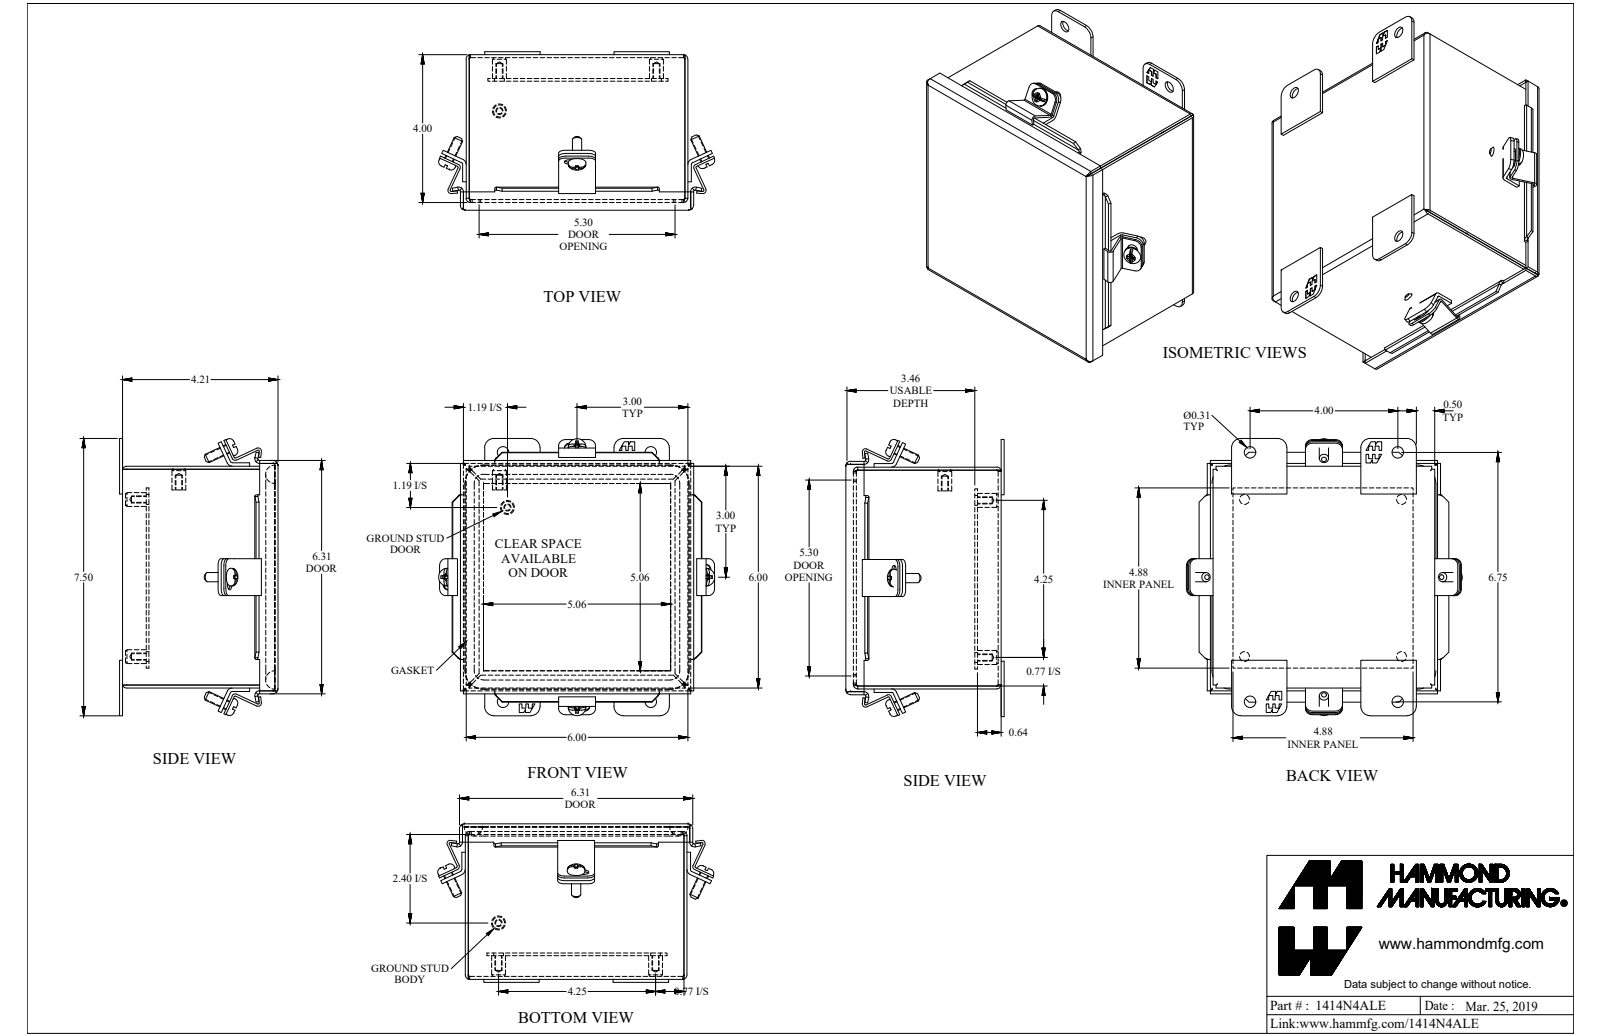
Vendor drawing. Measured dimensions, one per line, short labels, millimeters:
name: 1414N4ALE
written by: SolidWorks 2018 (AUTOMOTIVE_DESIGN)
unit: mm
bodies: 26 solids, 727 faces (499 planar, 162 cylindrical, 66 other)
size: 190.5 × 189.8 × 108.9
volume: 342 200 mm³; area: 343 600 mm²
holes: 6× ⌀4, 4× ⌀5.4, 4× ⌀6.7, 4× ⌀8
bosses: 6× ⌀9.5, 6× ⌀8.4, 4× ⌀12.2, 4× ⌀6.4
rounds: 12× R6.4, 8× R0.3, 8× R0.7, 8× R0.9, 8× R1.2, 8× R2.2, 8× R3, 8× R3.6
face distances: 2.1, 150.3, 104.8, 152.4, 148.3, 106.8, 102.7, 14.3, 16.3, 90.5
hole spacings: 108, 101.6, 102.5, 152.7, 171.5, 199.3, 7.9, 31.2
